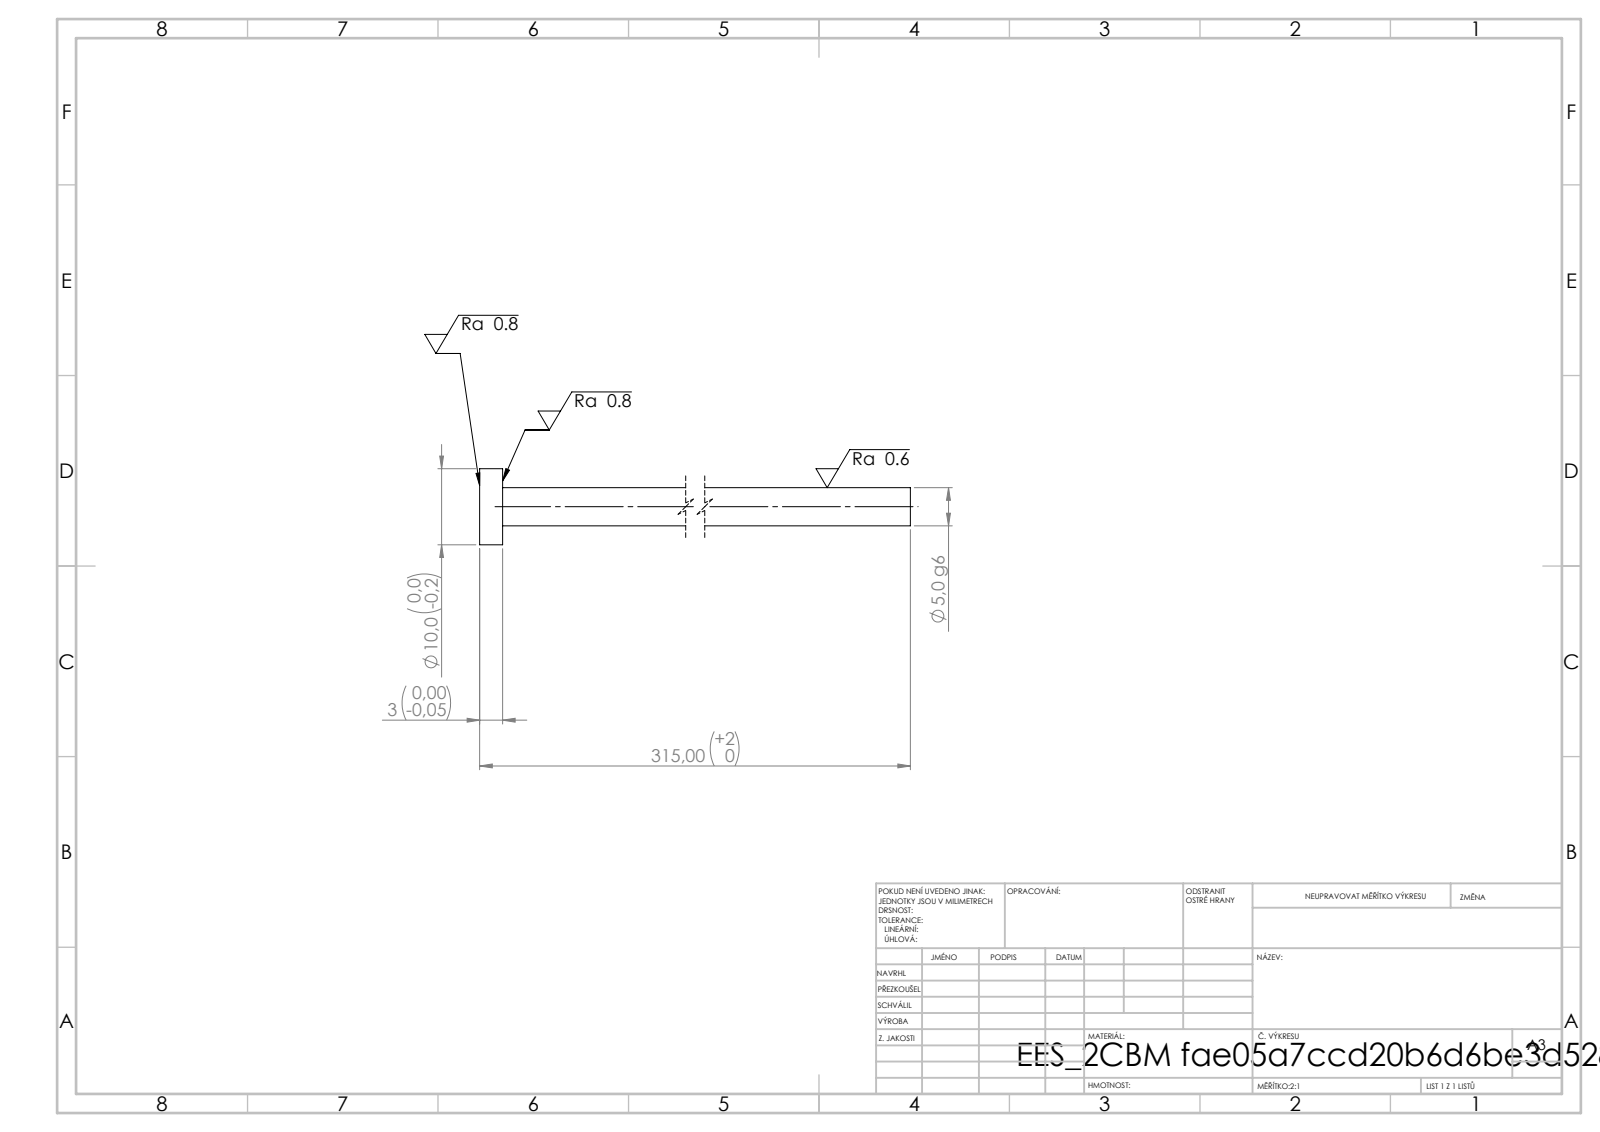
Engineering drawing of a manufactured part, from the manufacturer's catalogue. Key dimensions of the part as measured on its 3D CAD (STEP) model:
STEP written by: SolidWorks 2019 (CONFIG_CONTROL_DESIGN)
Units: millimetres
Bodies: 1 solid, 7 faces (3 planar, 4 cylindrical, 0 other)
Overall size (bounding box): 315 × 10 × 10
Volume: 6 362 mm³ · Surface area: 5 152 mm²
Round bosses / shafts (diameter × count): ⌀10 ×1, ⌀5 ×1
Main face-to-face distances: 3, 315, 312
